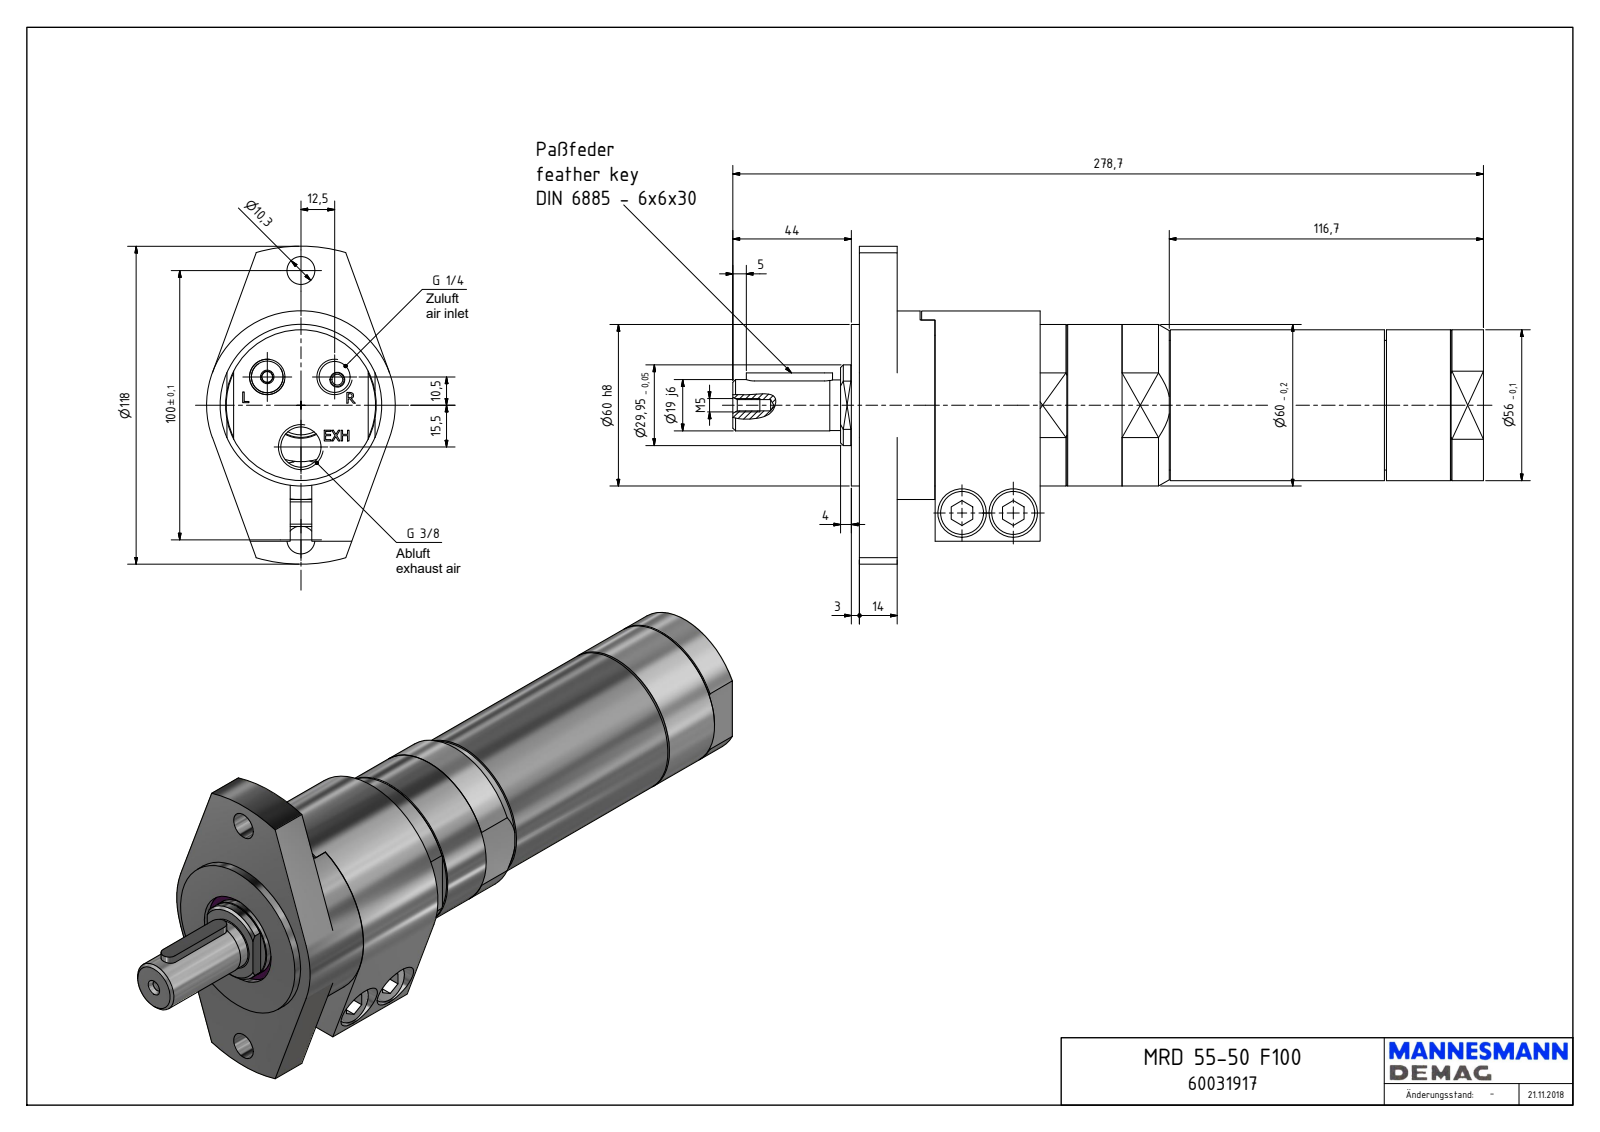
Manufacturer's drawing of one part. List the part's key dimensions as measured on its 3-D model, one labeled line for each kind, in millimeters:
Part name (STEP PRODUCT): MRD 55-50 F100_60031917
STEP written by: Autodesk Inventor 2018 (AUTOMOTIVE_DESIGN)
Units: millimetres
Bodies: 1 solid, 280 faces (164 planar, 63 cylindrical, 53 other)
Overall size (bounding box): 278.7 × 118 × 70
Volume: 748 926 mm³ · Surface area: 81 579 mm²
Round holes (diameter × count): ⌀4 ×2, ⌀8.38 ×2, ⌀10.3 ×2, ⌀10.5 ×2, ⌀18 ×2, ⌀1.55 ×1, ⌀4.13 ×1, ⌀5.5 ×1, ⌀11.45 ×1, ⌀14.95 ×1, ⌀35 ×1, ⌀40 ×1
Round bosses / shafts (diameter × count): ⌀16 ×2, ⌀10 ×2, ⌀70 ×1, ⌀60 ×1, ⌀56 ×1, ⌀55.18 ×1, ⌀48.18 ×1, ⌀29.95 ×1
Partial cylindrical surfaces — rounded edges, fillets, slot ends (radius × count): R3 ×2, R6 ×2, R5.72 ×1, R19.32 ×1, R23 ×1, R25.84 ×1, R59 ×1
Main face-to-face distances: 14, 17, 3, 231.7, 217.7, 234.7, 70.1, 67.1, 53.1, 164.6
Hole centre spacings: 16.32, 28.85, 41.43, 50, 61.78, 15.5, 19, 25
